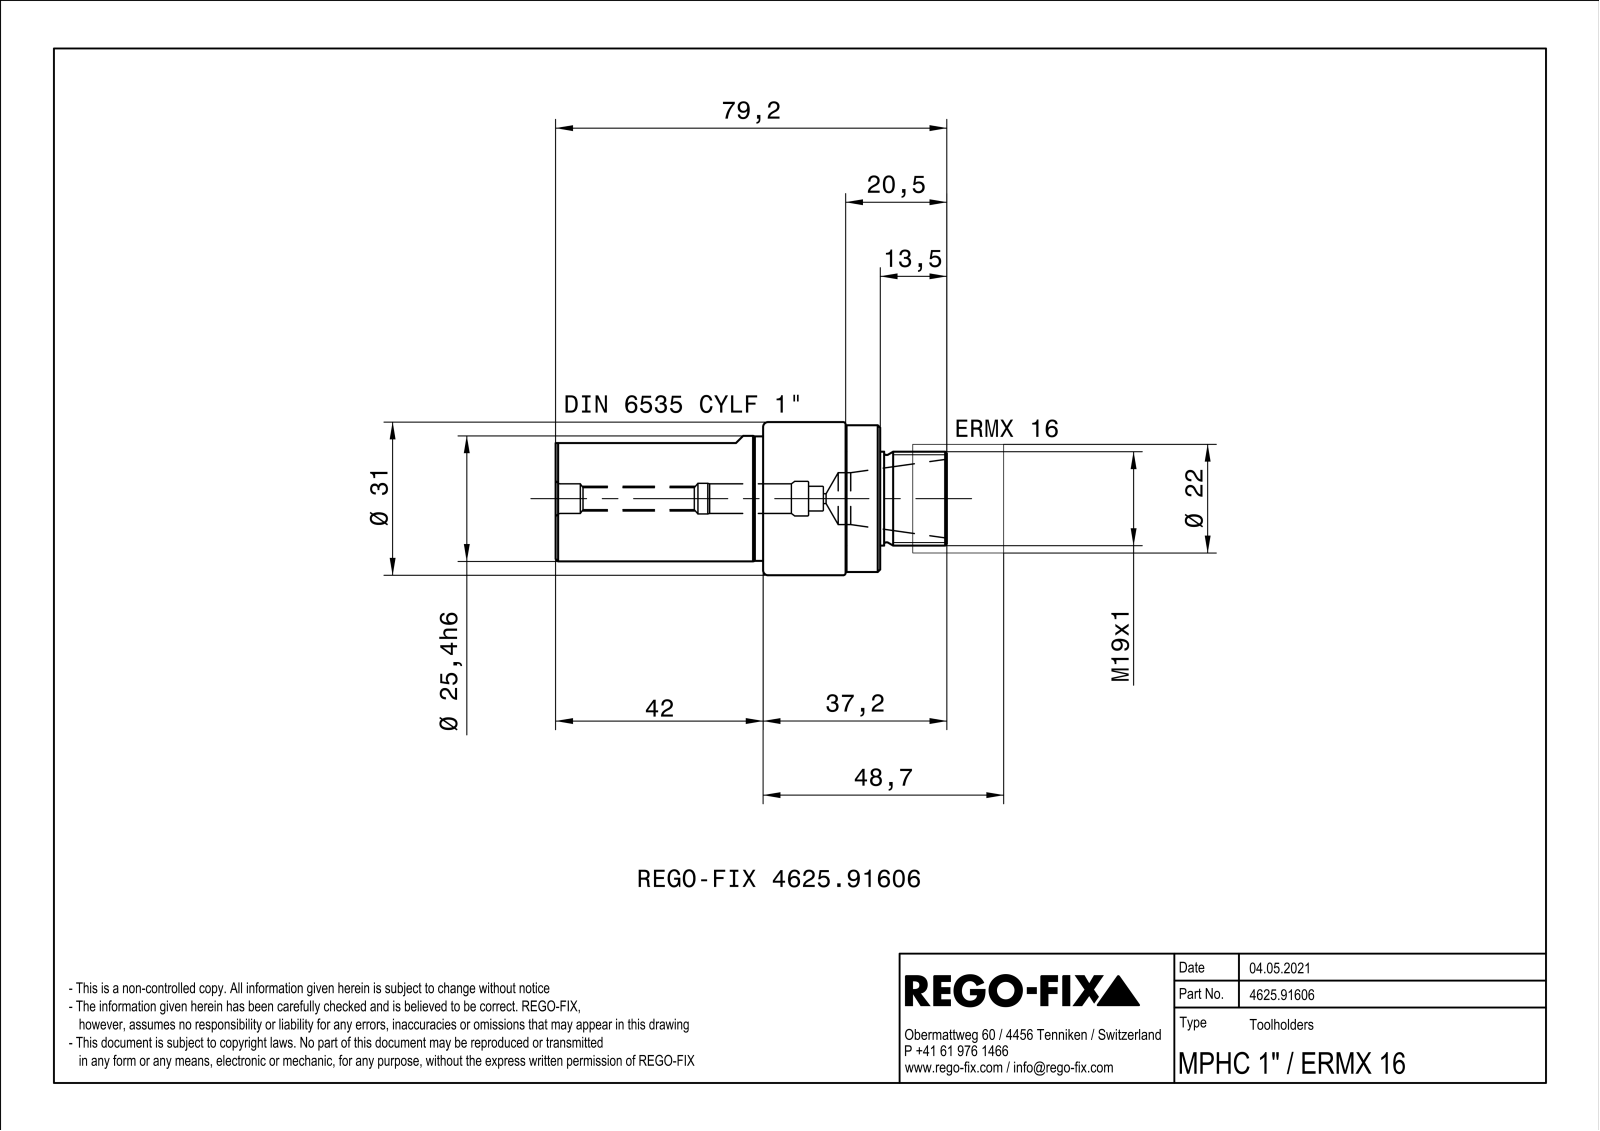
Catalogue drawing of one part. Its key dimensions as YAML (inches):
part_name: "NOCUT"
step_written_by: "SIEMENS PLM Software Solid Edge ST10 (AUTOMOTIVE_DESIGN)"
units: inches
bodies: {solids: 6, faces: 110, planar: 27, cylindrical: 35, other: 48}
overall_size: [3.118, 1.22, 1.22]
volume: 2.122
surface_area: 27.06
round_holes:
  - {diameter: 0.098, count: 4}
  - {diameter: 0.098, count: 2}
  - {diameter: 0.062, count: 1}
  - {diameter: 0.079, count: 1}
  - {diameter: 0.176, count: 1}
  - {diameter: 0.197, count: 1}
  - {diameter: 0.236, count: 1}
  - {diameter: 0.244, count: 1}
  - {diameter: 0.276, count: 1}
  - {diameter: 0.413, count: 1}
  - {diameter: 0.787, count: 1}
  - {diameter: 1.063, count: 1}
round_bosses_or_shafts:
  - {diameter: 1.22, count: 1}
  - {diameter: 1.169, count: 1}
  - {diameter: 1.102, count: 1}
  - {diameter: 1.024, count: 1}
  - {diameter: 1, count: 1}
  - {diameter: 0.992, count: 1}
  - {diameter: 0.748, count: 1}
  - {diameter: 0.736, count: 1}
face_to_face_distances: [0.657, 0.236, 0.079, 2.547, 1.89, 0.531, 0.421, 2.311, 0.571, 0.295]
hole_center_spacings: [0.453, 0.64, 0.906]
